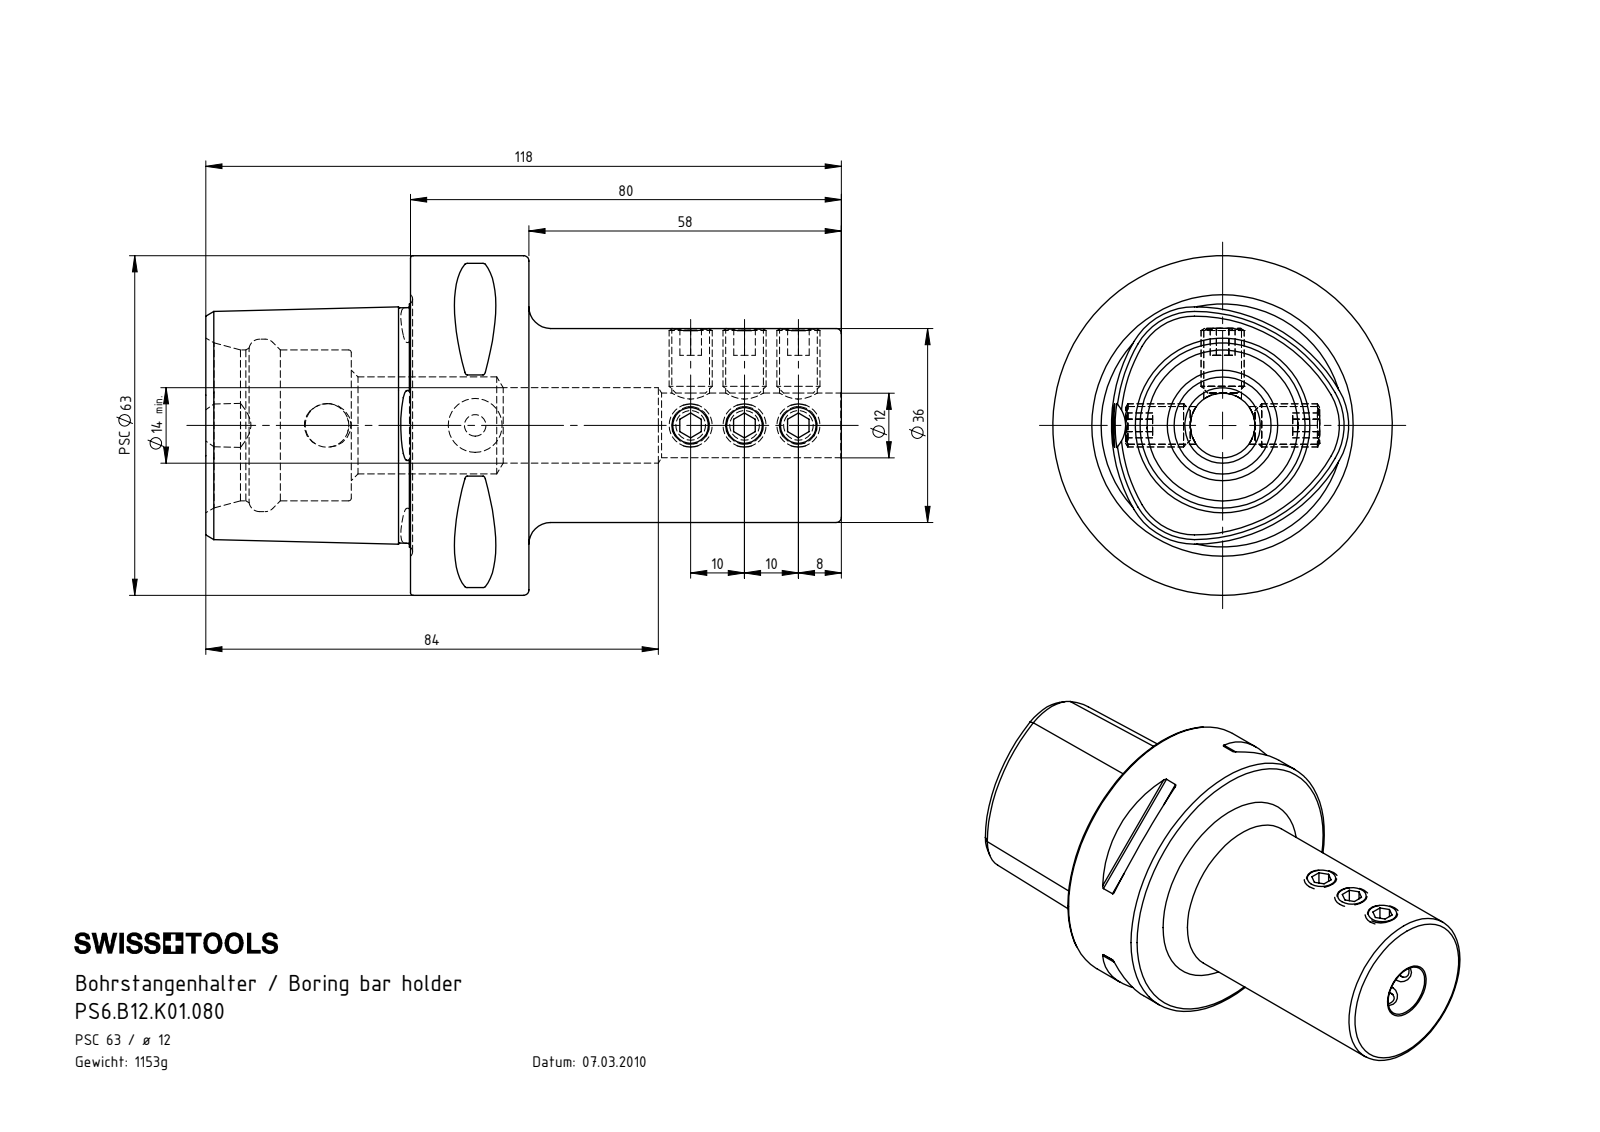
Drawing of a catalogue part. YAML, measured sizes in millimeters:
part_name: "ISO 4026 - M8 x 12; ISO 4026 - M8 x 12_PreviewCfg; PS6.B12.K01.080; PS6-B12.K01.080_A"
step_written_by: "SolidWorks 2017 (AUTOMOTIVE_DESIGN)"
units: millimeters
bodies: {solids: 10, faces: 285, planar: 101, cylindrical: 67, other: 117}
overall_size: [118, 63, 63]
volume: 147292
surface_area: 34250
round_holes:
  - {diameter: 7, count: 6}
  - {diameter: 4, count: 1}
  - {diameter: 8.1, count: 1}
  - {diameter: 12, count: 1}
  - {diameter: 14, count: 1}
  - {diameter: 18, count: 1}
  - {diameter: 28, count: 1}
  - {diameter: 32, count: 1}
round_bosses_or_shafts:
  - {diameter: 8, count: 6}
  - {diameter: 63, count: 1}
  - {diameter: 36, count: 1}
partial_cylinders:
  - {radius: 0.5, count: 8}
  - {radius: 6, count: 1}
face_to_face_distances: [22, 80, 58, 38, 60, 118, 5, 4, 10, 24.88]
hole_center_spacings: [10, 20, 27.5, 40, 50, 60, 67.5, 77.5]
